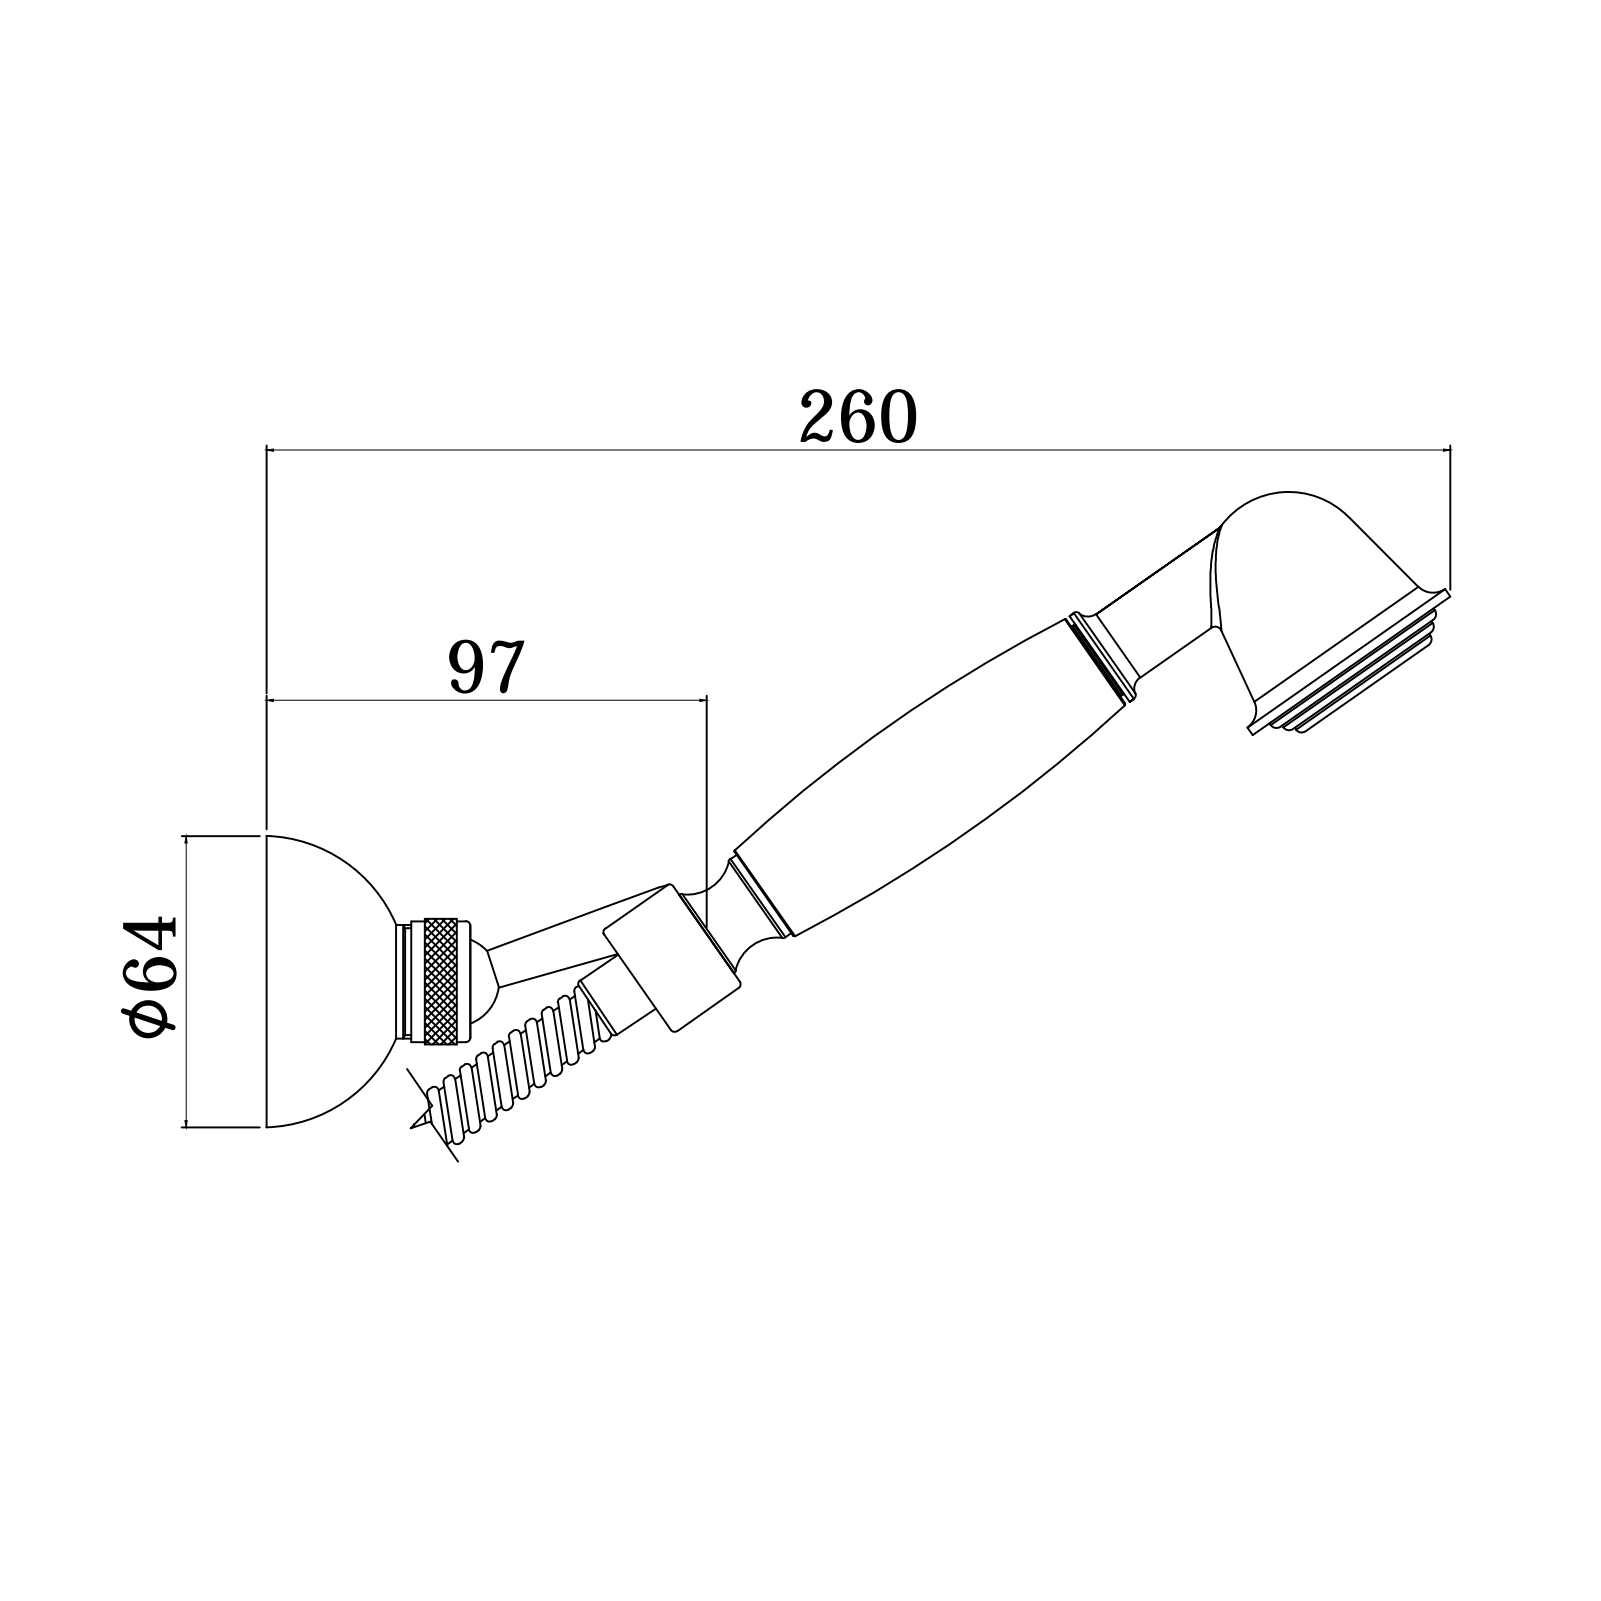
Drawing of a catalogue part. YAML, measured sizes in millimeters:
part_name: "ZDUP011CR"
step_written_by: "CREO PARAMETRIC BY PTC INC, 2020044 (CONFIG_CONTROL_DESIGN)"
units: millimeters
bodies: {solids: 1, faces: 257, planar: 51, cylindrical: 58, other: 148}
overall_size: [241.11, 225.71, 63]
volume: 160278
surface_area: 63095
round_holes:
  - {diameter: 6, count: 1}
  - {diameter: 14.5, count: 1}
  - {diameter: 18, count: 1}
  - {diameter: 19, count: 1}
  - {diameter: 21, count: 1}
  - {diameter: 23.5, count: 1}
  - {diameter: 34.4, count: 1}
  - {diameter: 38.4, count: 1}
  - {diameter: 42.4, count: 1}
  - {diameter: 46.4, count: 1}
round_bosses_or_shafts:
  - {diameter: 53, count: 1}
  - {diameter: 44, count: 1}
  - {diameter: 40, count: 1}
  - {diameter: 36, count: 1}
  - {diameter: 29, count: 1}
  - {diameter: 27, count: 1}
  - {diameter: 26, count: 1}
  - {diameter: 24.5, count: 1}
partial_cylinders:
  - {radius: 10, count: 1}
face_to_face_distances: [0.5, 6, 2.5, 8.5, 5.5, 2, 8, 4, 6.5, 1.5]
